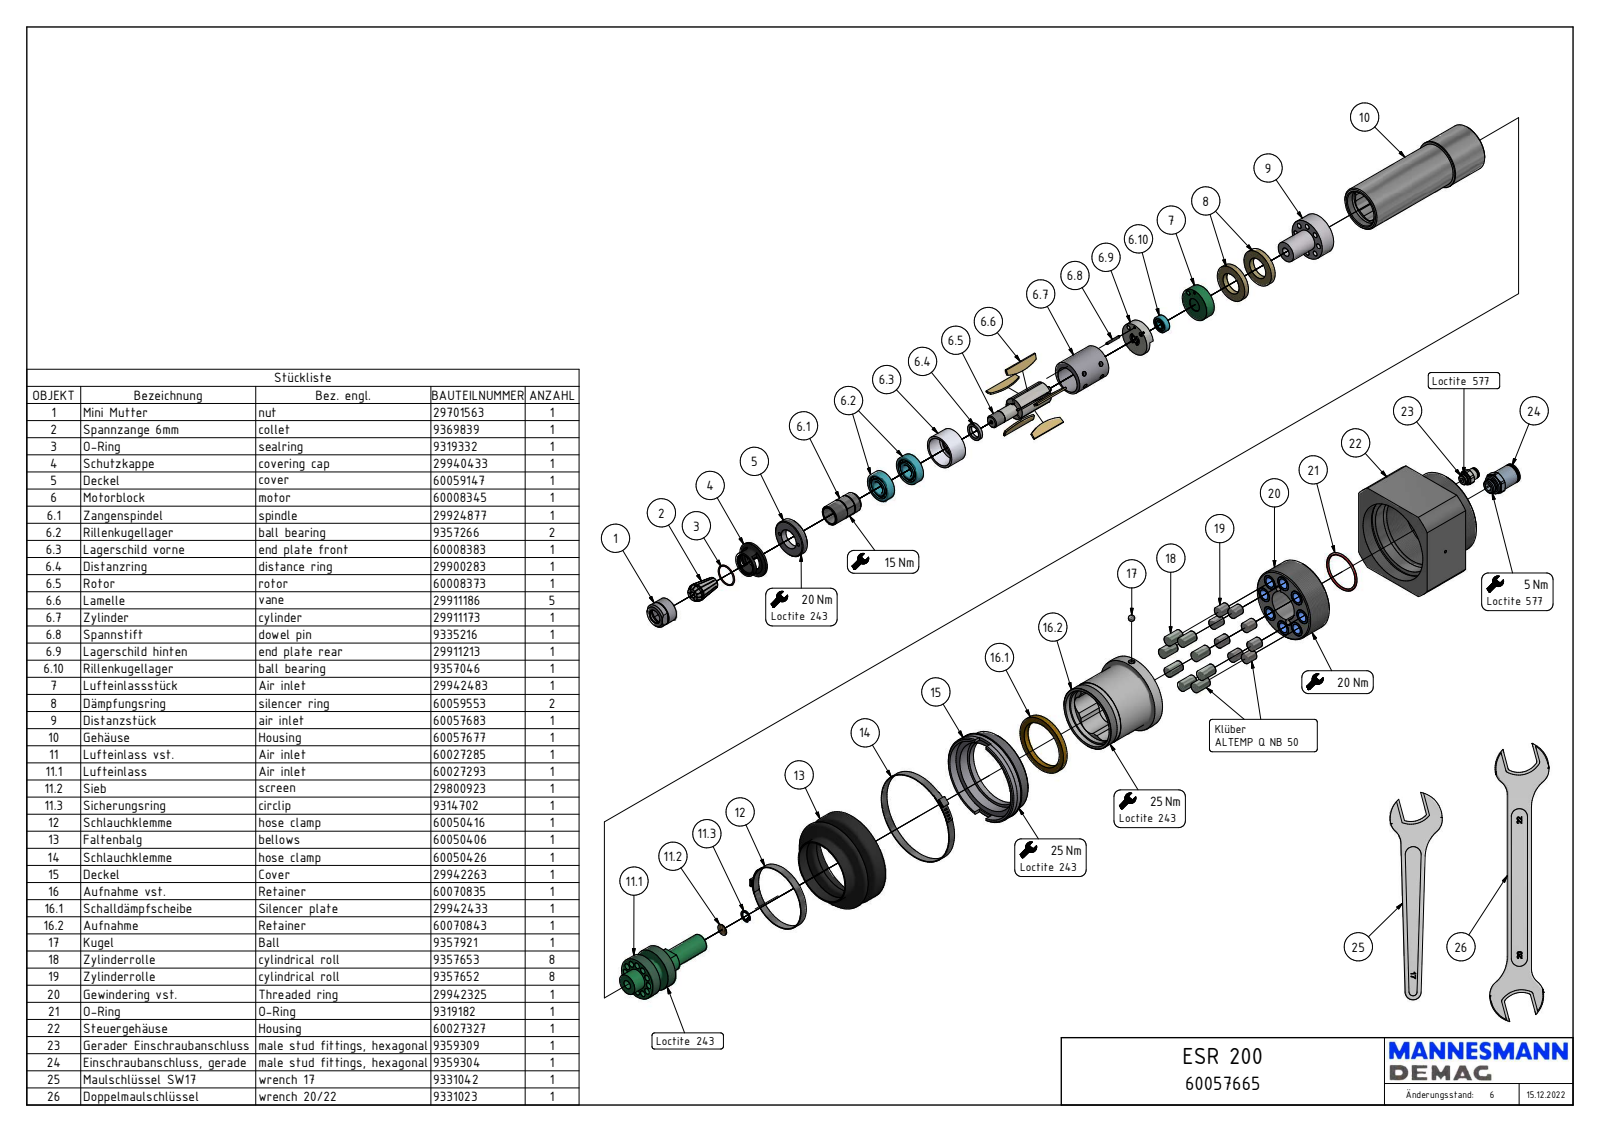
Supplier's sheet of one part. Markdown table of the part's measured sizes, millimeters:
| quantity | value |
| --- | --- |
| part name | ESR 200_60057665 |
| STEP written by | Autodesk Inventor 2018 (AUTOMOTIVE_DESIGN) |
| units | millimeters |
| bodies | 1 solid, 481 faces (203 planar, 152 cylindrical, 126 other) |
| overall size | 277.39 × 90 × 90 |
| volume | 833 907 mm³ |
| surface area | 87 841 mm² |
| round holes (diameter × count) | 4.92 × 4, 6 × 4, 3 × 2, 6 × 2, 1.6 × 1, 2.5 × 1, 8.5 × 1, 8.57 × 1, 11 × 1, 11.45 × 1, 12 × 1, 12.2 × 1 |
| round bosses / shafts (diameter × count) | 89.2 × 1, 88 × 1, 80 × 1, 78.18 × 1, 63.2 × 1, 62 × 1, 60 × 1, 59.72 × 1 |
| partial cylindrical surfaces (radius × count) | 0.5 × 8, 1 × 8, 1.1 × 8, 18.09 × 6, 33.72 × 6, 1.4 × 4, 2 × 4, 3.05 × 1 |
| main face-to-face distances | 90, 20, 50.5, 70.5, 0.5, 41, 91.5, 111.5, 10, 7 |
| hole center spacings | 19, 59.14, 56, 12.25, 28.04, 33.02, 34.7, 38 |
